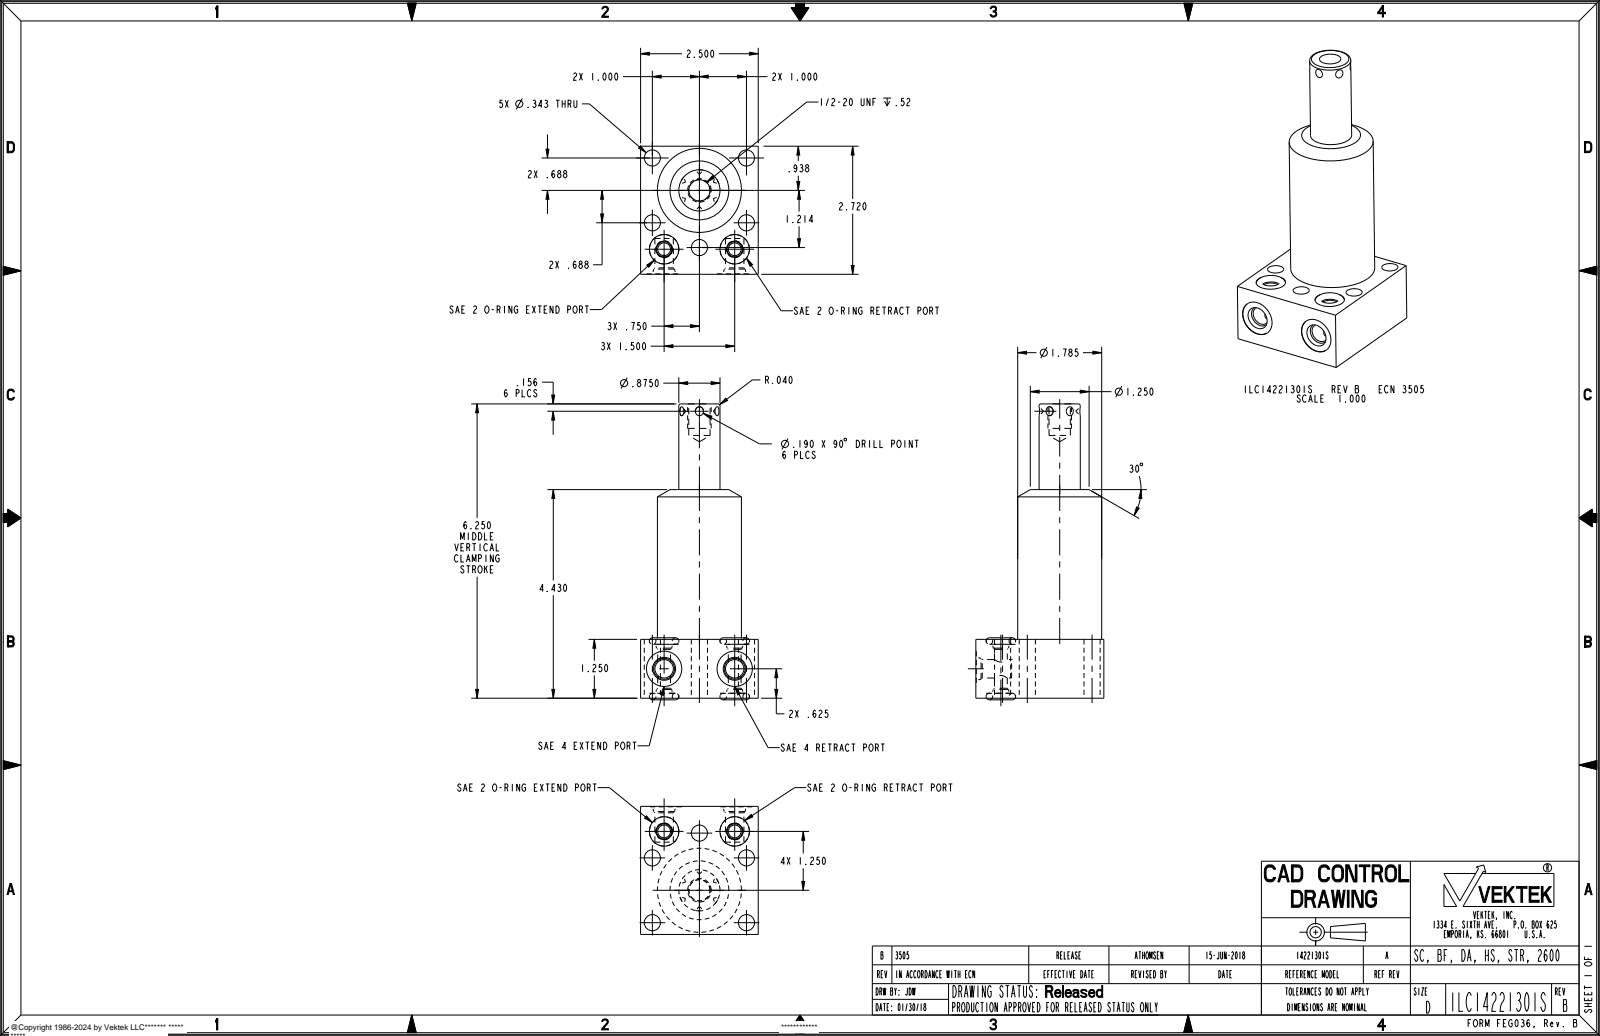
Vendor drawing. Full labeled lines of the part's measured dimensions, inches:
Part name (STEP PRODUCT): ILC14221301S
STEP written by: PRO/ENGINEER BY PARAMETRIC TECHNOLOGY CORPORATION, 2013320 (AUTOMOTIVE_DESIGN)
Units: inches
Bodies: 5 solids, 117 faces (17 planar, 42 cylindrical, 58 other)
Overall size (bounding box): 6.284 × 2.72 × 2.5
Volume: 16.42 in³ · Surface area: 62.49 in²
Round holes (diameter × count): ⌀0.343 ×5, ⌀0.272 ×2, ⌀0.392 ×2, ⌀0.625 ×2, ⌀0.75 ×2, ⌀0.453 ×1
Round bosses / shafts (diameter × count): ⌀1.785 ×1, ⌀0.875 ×1, ⌀0.5 ×1
Main face-to-face distances: 2.5, 1.25, 2.72, 0.105, 1.145, 4.43, 3.18, 2.71, 1.04, 4.325
Hole centre spacings: 1.214, 0.615, 0.751, 1.13, 1.376, 1.458, 1.5, 1.838
